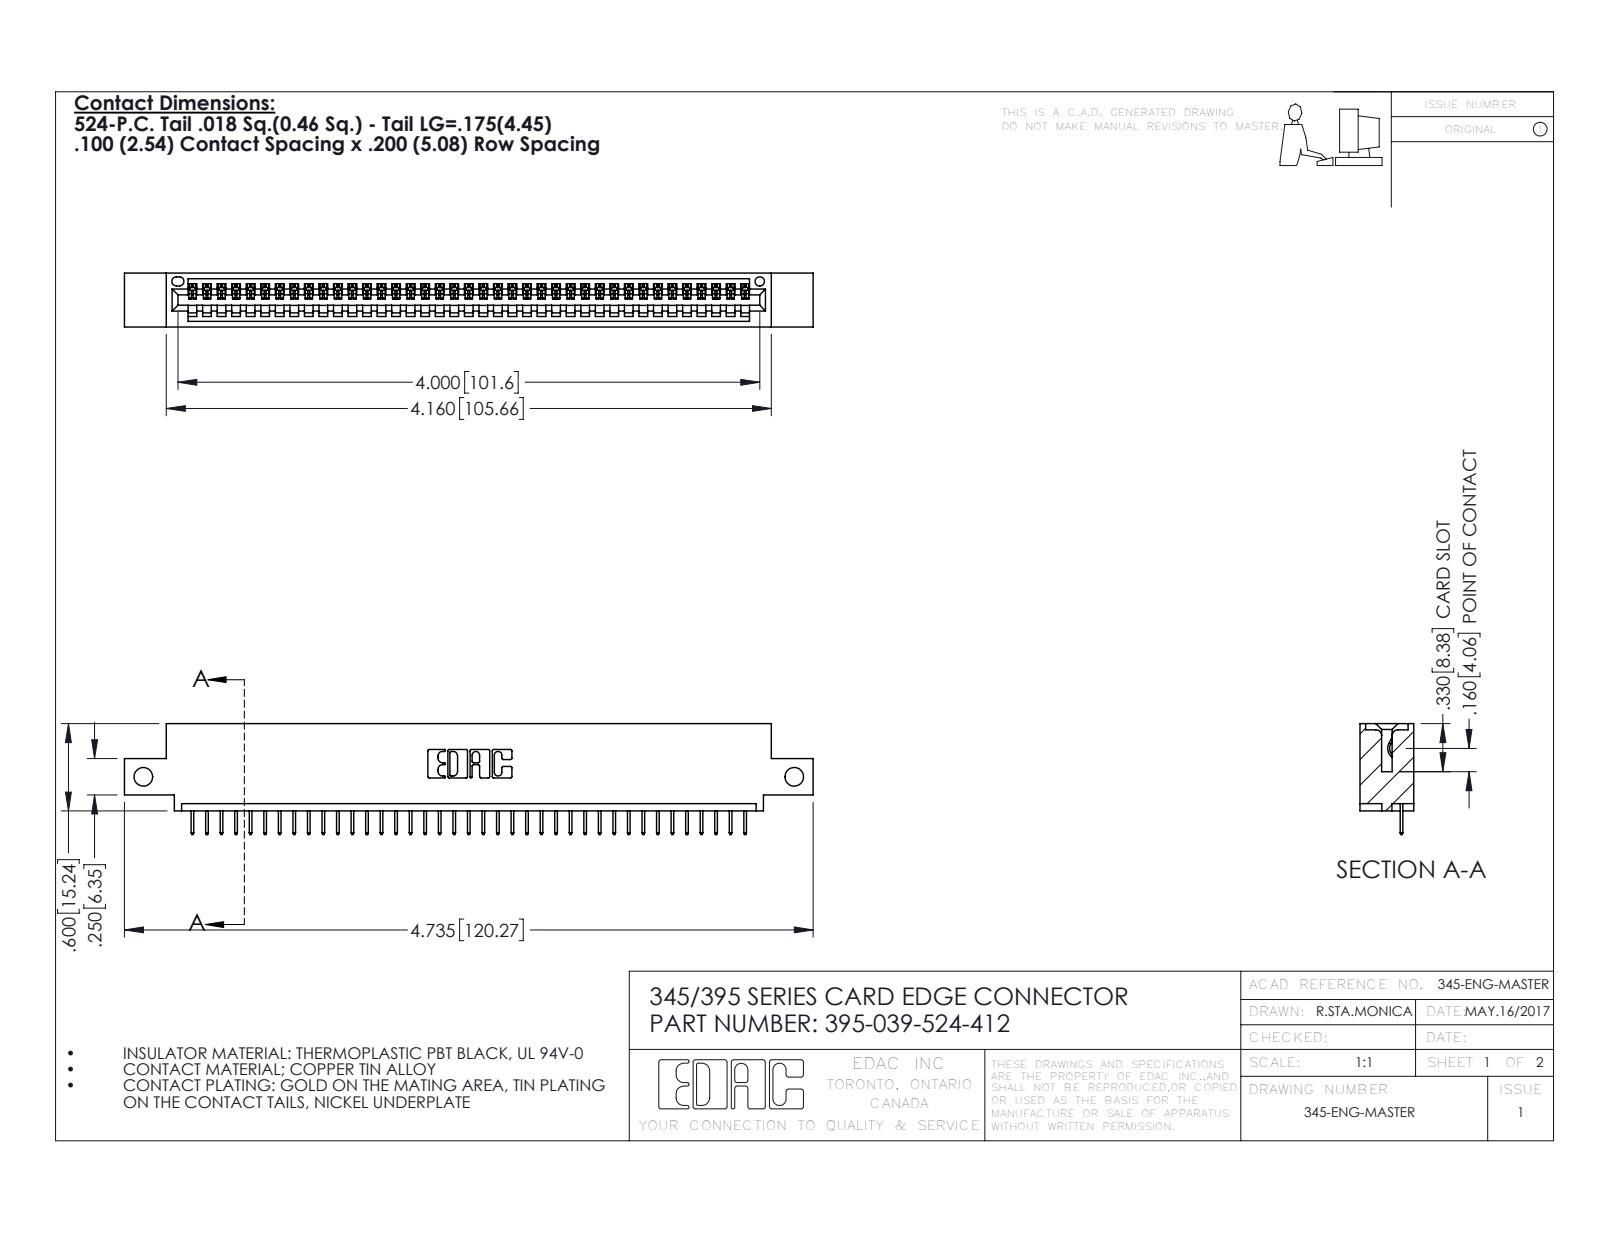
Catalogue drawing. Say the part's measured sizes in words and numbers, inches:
The part is named "345-292-001_345-293-124; 345 Part_0.110 Offset - Side Mount; 395-039-524-412". Its 3-D file was written by "SolidWorks 2016 (CONFIG_CONTROL_DESIGN)". It is 40 solids with 2548 faces: 1878 planar, 670 cylindrical and 0 other. Overall it measures 4.735 by 0.762 by 0.37 inches. Its volume is 0.676 cubic inches and its surface area 21.91 square inches. Round holes: 2 of diameter 0.128, 1 of diameter 0.064. Partial cylindrical surfaces (rounded edges, fillets, slot ends): 78 of radius 0.006, 22 of radius 0.01, 6 of radius 0.007, 6 of radius 0.031, 3 of radius 0.026, 2 of radius 0.031, 2 of radius 0.04, 1 of radius 0.014. The main face-to-face distances are 0.072, 0.298, 0.37, 0.2, 0.098, 0.272, 0.025, 0.225, 0.072, 0.149. The hole center spacings are 4.475.
